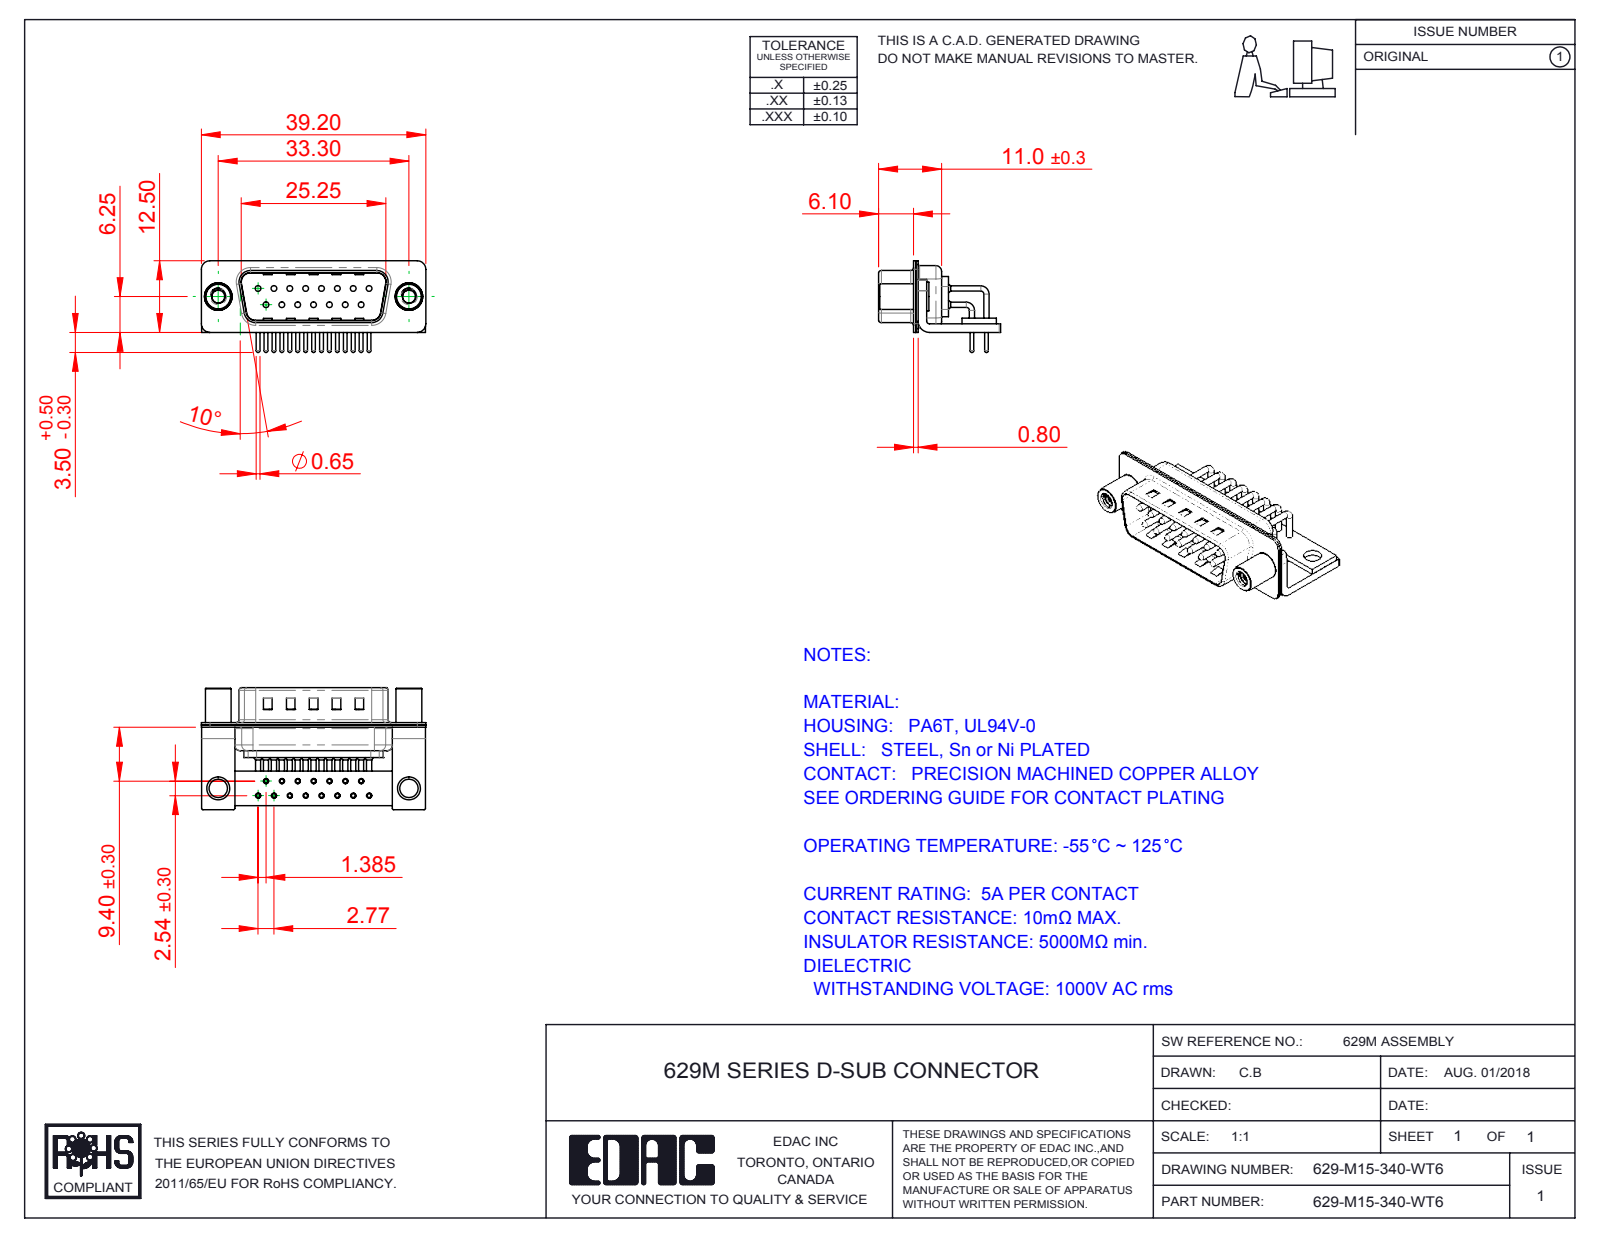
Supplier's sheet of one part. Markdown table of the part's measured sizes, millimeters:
| quantity | value |
| --- | --- |
| part name | 629M 4-40 Threaded Standoff; 629M Housing_15 Contacts; 629M Stabilizer Board_15 Contacts; 629M Shell Front_15 Contacts (+5 more) |
| STEP written by | SolidWorks 2016 (CONFIG_CONTROL_DESIGN) |
| units | millimeters |
| bodies | 23 solids, 2120 faces (1127 planar, 767 cylindrical, 226 other) |
| overall size | 39.2 × 21.3 × 16 |
| volume | 2 563 mm³ |
| surface area | 6 845 mm² |
| round holes (diameter × count) | 0.9 × 15, 1 × 15, 1.7 × 15, 2 × 15, 2.26 × 2, 3.2 × 2, 4 × 2, 4.8 × 2 |
| round bosses / shafts (diameter × count) | 0.9 × 21, 1.5 × 15, 0.65 × 15, 5 × 2, 4.9 × 2, 4.5 × 2 |
| partial cylindrical surfaces (radius × count) | 0.25 × 16, 1.5 × 16, 1.01 × 15, 2 × 13, 0.5 × 9, 1.6 × 8, 0.6 × 4, 0.65 × 4 |
| main face-to-face distances | 0.4, 1.5, 0.85, 0.8, 1.25, 10.4, 9.55, 1.9, 1, 8.3 |
| hole center spacings | 2.77, 5.54, 3.16, 8.31, 4.87, 11.08, 2.89, 7.37 |
